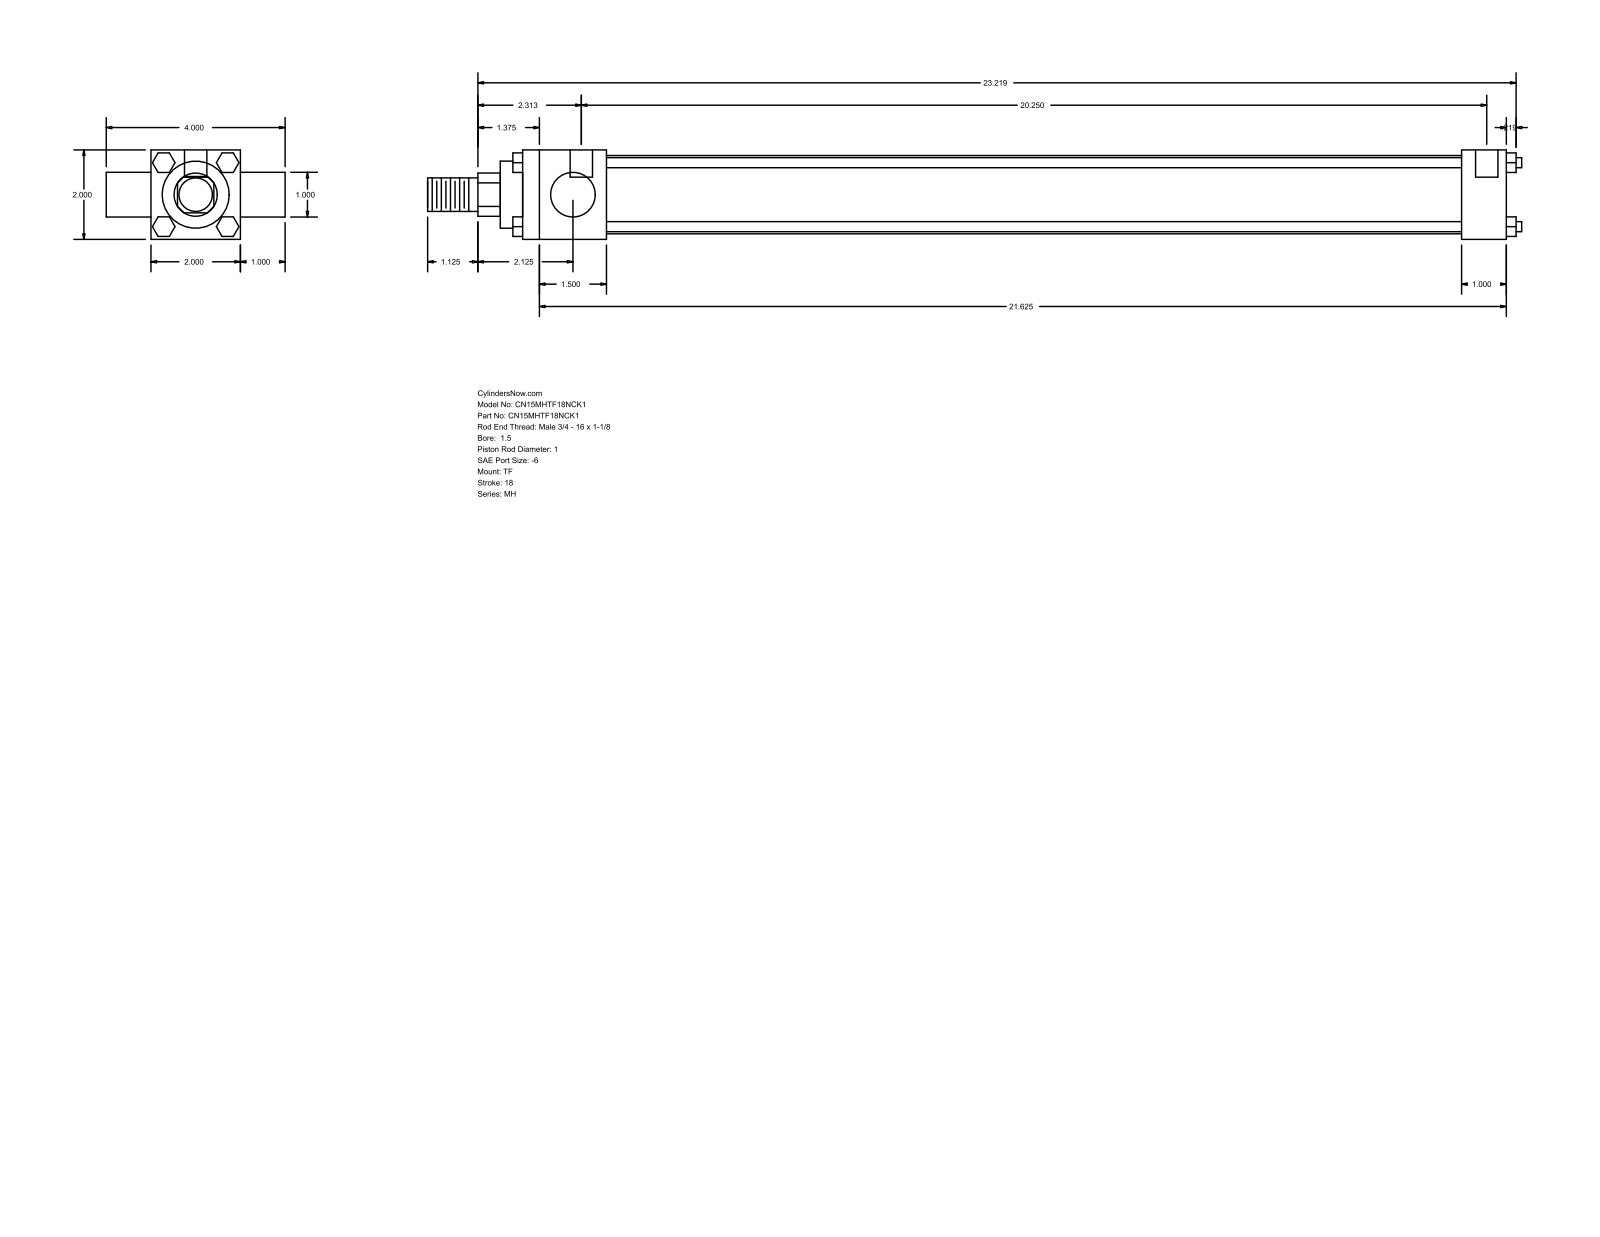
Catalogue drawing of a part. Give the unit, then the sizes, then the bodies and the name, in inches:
Units: inches
Overall size (bounding box): 24.469 × 4 × 2
Round holes (diameter × count): ⌀0.219 ×3, ⌀0.5 ×2
Round bosses / shafts (diameter × count): ⌀0.225 ×4, ⌀1 ×2, ⌀1.75 ×1, ⌀1.5 ×1, ⌀0.75 ×1
Partial cylindrical surfaces — rounded edges, fillets, slot ends (radius × count): R0.484 ×1
Main face-to-face distances: 2, 1, 22, 3, 1.875, 20.125, 21, 19.125, 4, 0.5
Hole centre spacings: 0.125, 20.25, 20.375
Bodies: 0 solids, 120 faces (92 planar, 28 cylindrical, 0 other)
Part name (STEP PRODUCT): MH_TF__0150_1
STEP written by: GSSL Pune (CONFIG_CONTROL_DESIGN)
